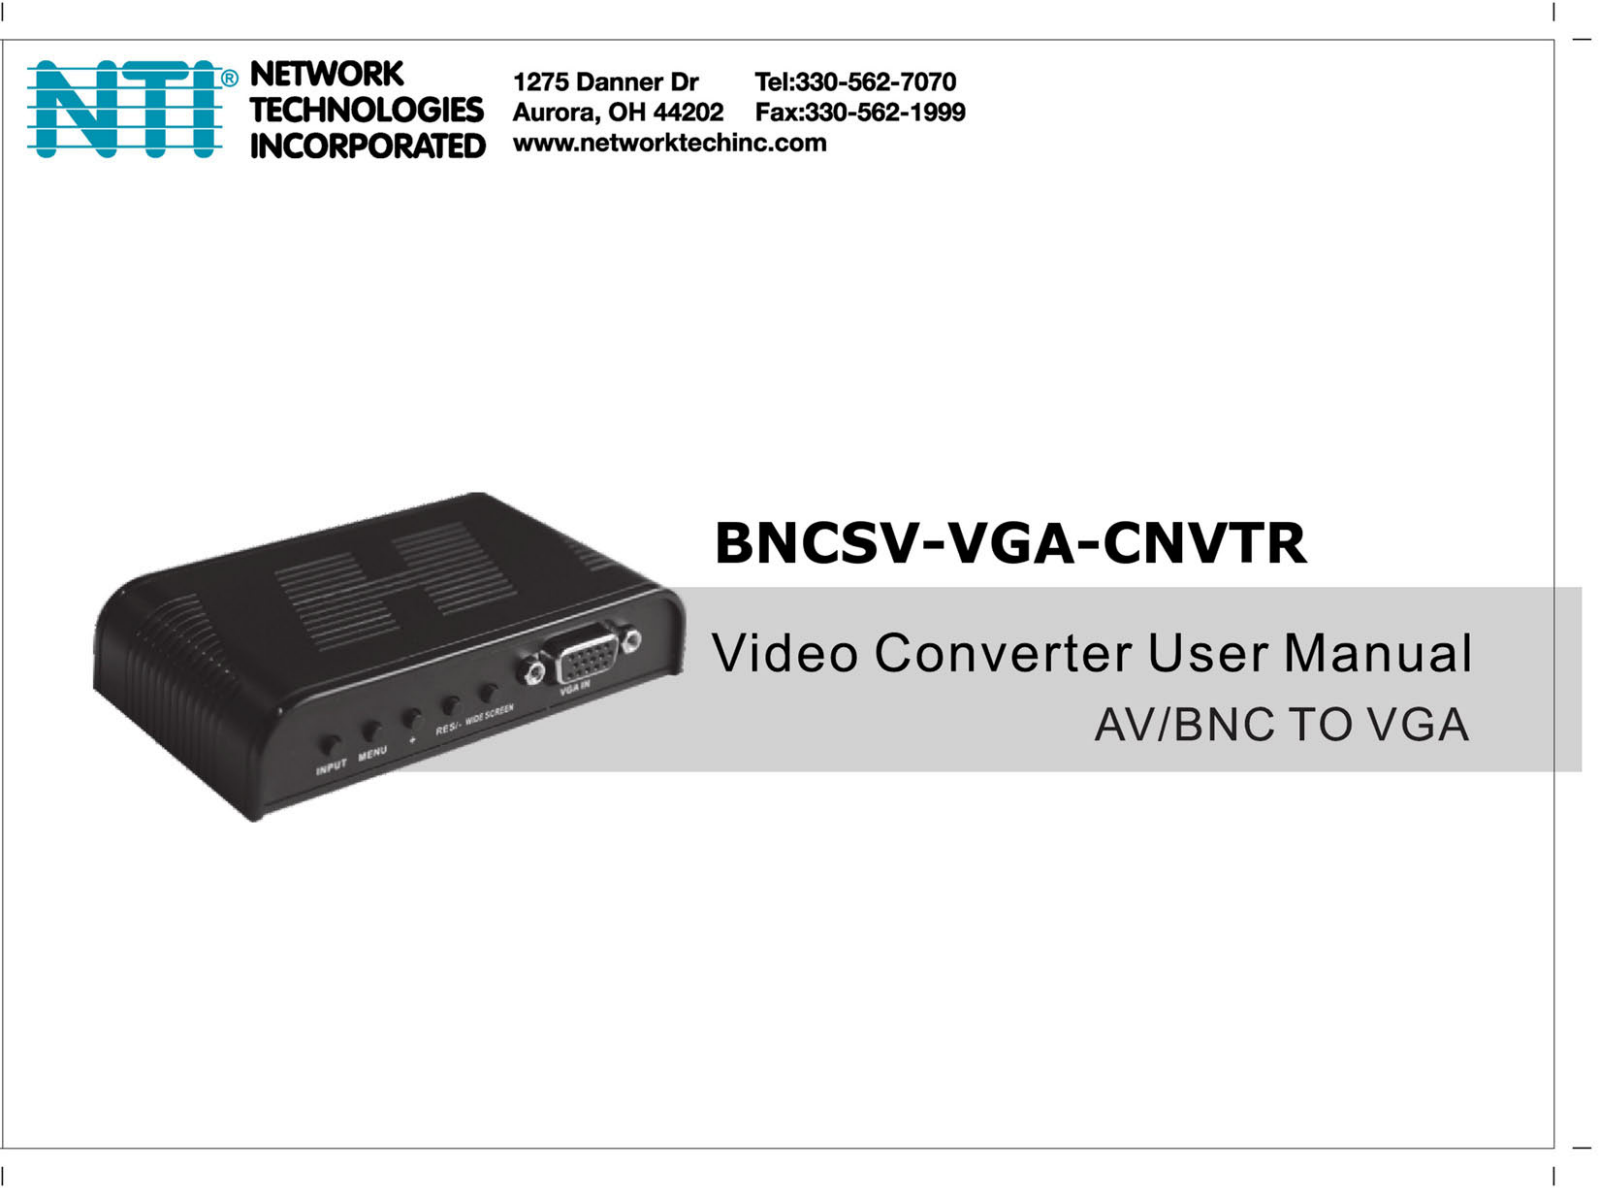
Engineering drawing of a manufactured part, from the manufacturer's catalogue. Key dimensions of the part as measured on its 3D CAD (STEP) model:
Part name (STEP PRODUCT): BNCSV-VGA-CNVTR-MDP (BNCSV-VGA-CNVTR); RCA___1_5; GG; BNC_RA (+5 more)
STEP written by: SolidWorks 2011 (AUTOMOTIVE_DESIGN)
Units: millimetres
Bodies: 13 solids, 2664 faces (1028 planar, 534 cylindrical, 1102 other)
Overall size (bounding box): 104.89 × 69.94 × 22.5
Round holes (diameter × count): ⌀0.8 ×30, ⌀1.7 ×4, ⌀1.82 ×4, ⌀2.5 ×4, ⌀0.84 ×1, ⌀3.4 ×1, ⌀6.4 ×1, ⌀9 ×1, ⌀11.54 ×1, ⌀12.14 ×1, ⌀13.4 ×1
Round bosses / shafts (diameter × count): ⌀1.09 ×6, ⌀3.2 ×5, ⌀3.18 ×4, ⌀13 ×1, ⌀11.94 ×1, ⌀11.66 ×1, ⌀10.9 ×1, ⌀9.8 ×1
Partial cylindrical surfaces — rounded edges, fillets, slot ends (radius × count): R0.2 ×195, R0.54 ×46, R0.3 ×32, R0.1 ×16, R1 ×12, R2.29 ×6, R0.5 ×2, R2.24 ×2
Main face-to-face distances: 2.1, 20.4, 18.3, 22.5, 53.84, 55.94, 51.74, 1.6, 6.4, 0.5
Hole centre spacings: 2.29, 3.96, 6.05, 2.28, 4.57, 4.58, 6.86, 6.87
